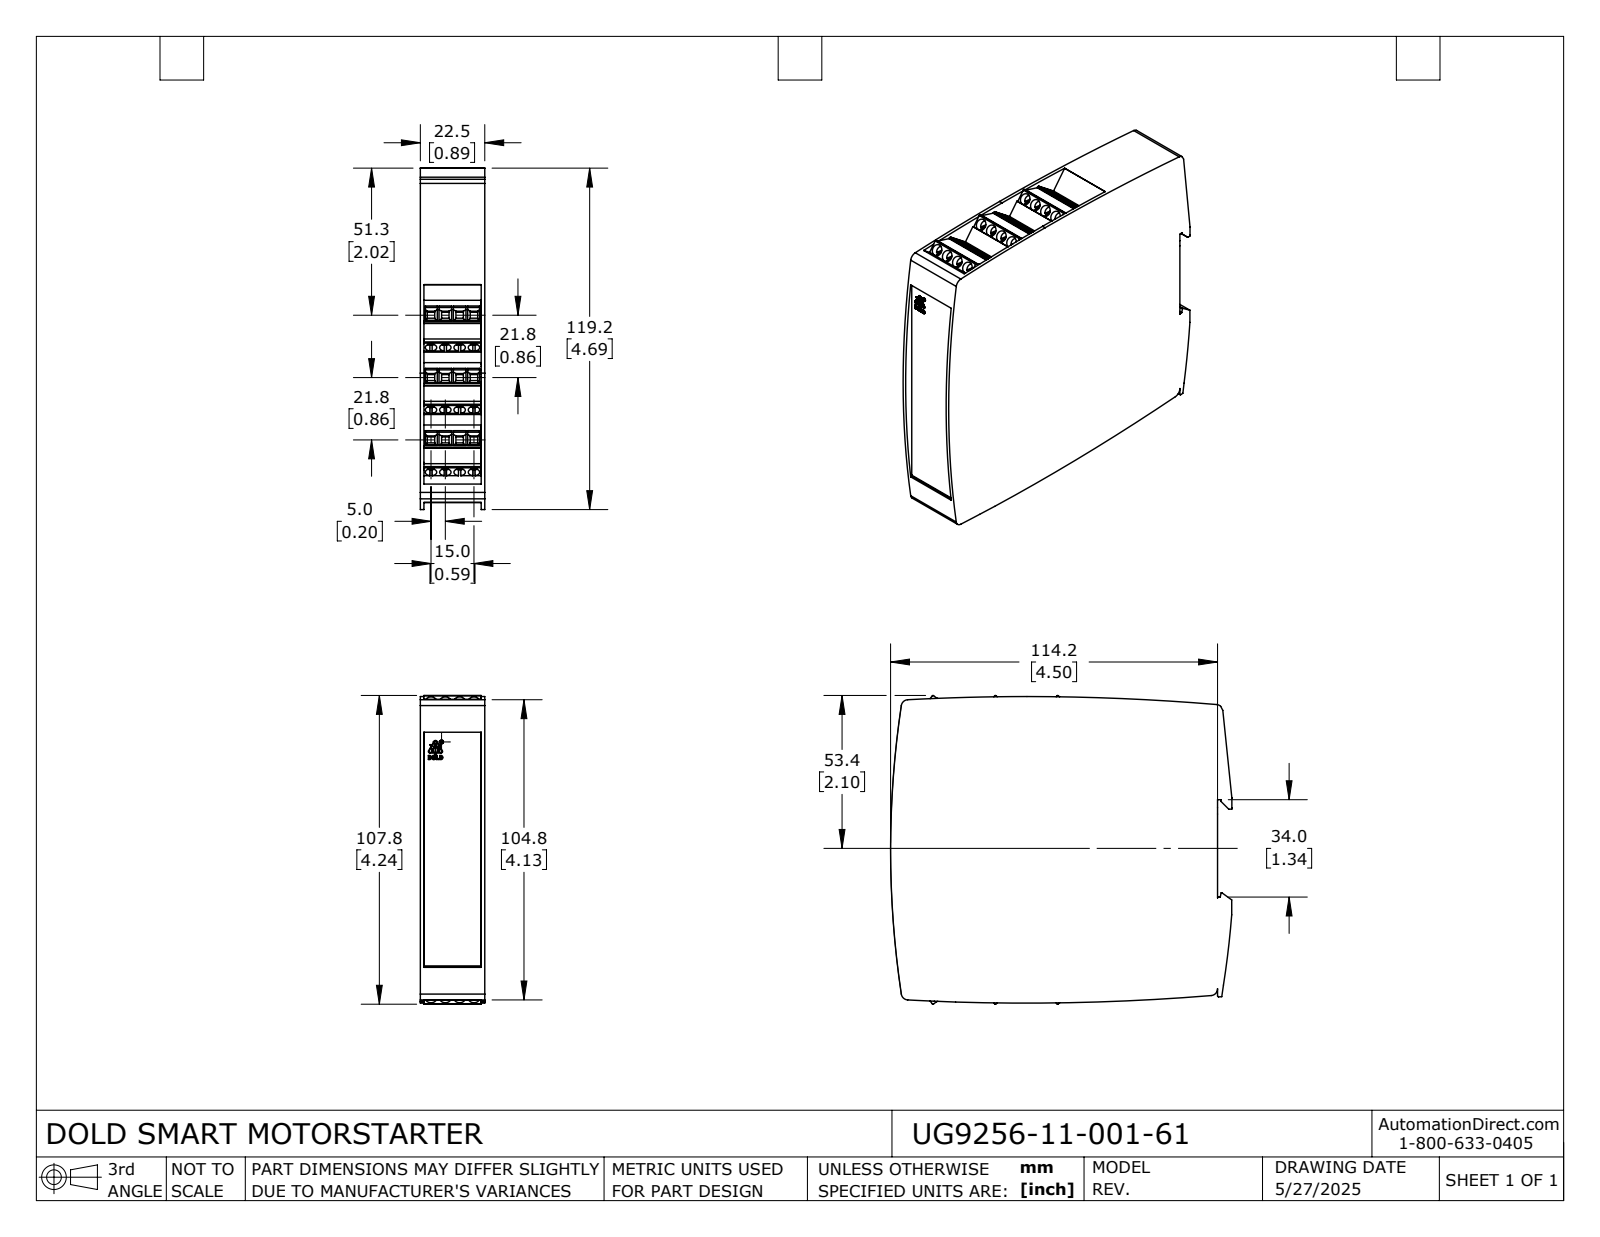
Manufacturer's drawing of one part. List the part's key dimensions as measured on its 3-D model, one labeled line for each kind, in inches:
Part name (STEP PRODUCT): UG9256-11-001-61
STEP written by: SolidWorks 2024 (AUTOMOTIVE_DESIGN)
Units: inches
Bodies: 1 solid, 1036 faces (813 planar, 222 cylindrical, 1 other)
Overall size (bounding box): 4.693 × 4.243 × 0.886
Volume: 15.85 in³ · Surface area: 64.72 in²
Round holes (diameter × count): ⌀0.157 ×24, ⌀0.053 ×1
Round bosses / shafts (diameter × count): ⌀0.15 ×24, ⌀0.049 ×1
Partial cylindrical surfaces — rounded edges, fillets, slot ends (radius × count): R0.012 ×15, R0.02 ×14, R0.004 ×12, R0.094 ×7, R0.005 ×6, R0.004 ×4, R31.496 ×4, R0.021 ×3
Main face-to-face distances: 0.886, 0.049, 0.837, 0.675, 4.379, 0.051, 0.835, 1.35, 0.528, 0.785
Hole centre spacings: 0.563, 0.197, 0.528, 0.658, 0.394, 1.073, 0.792, 1.055
